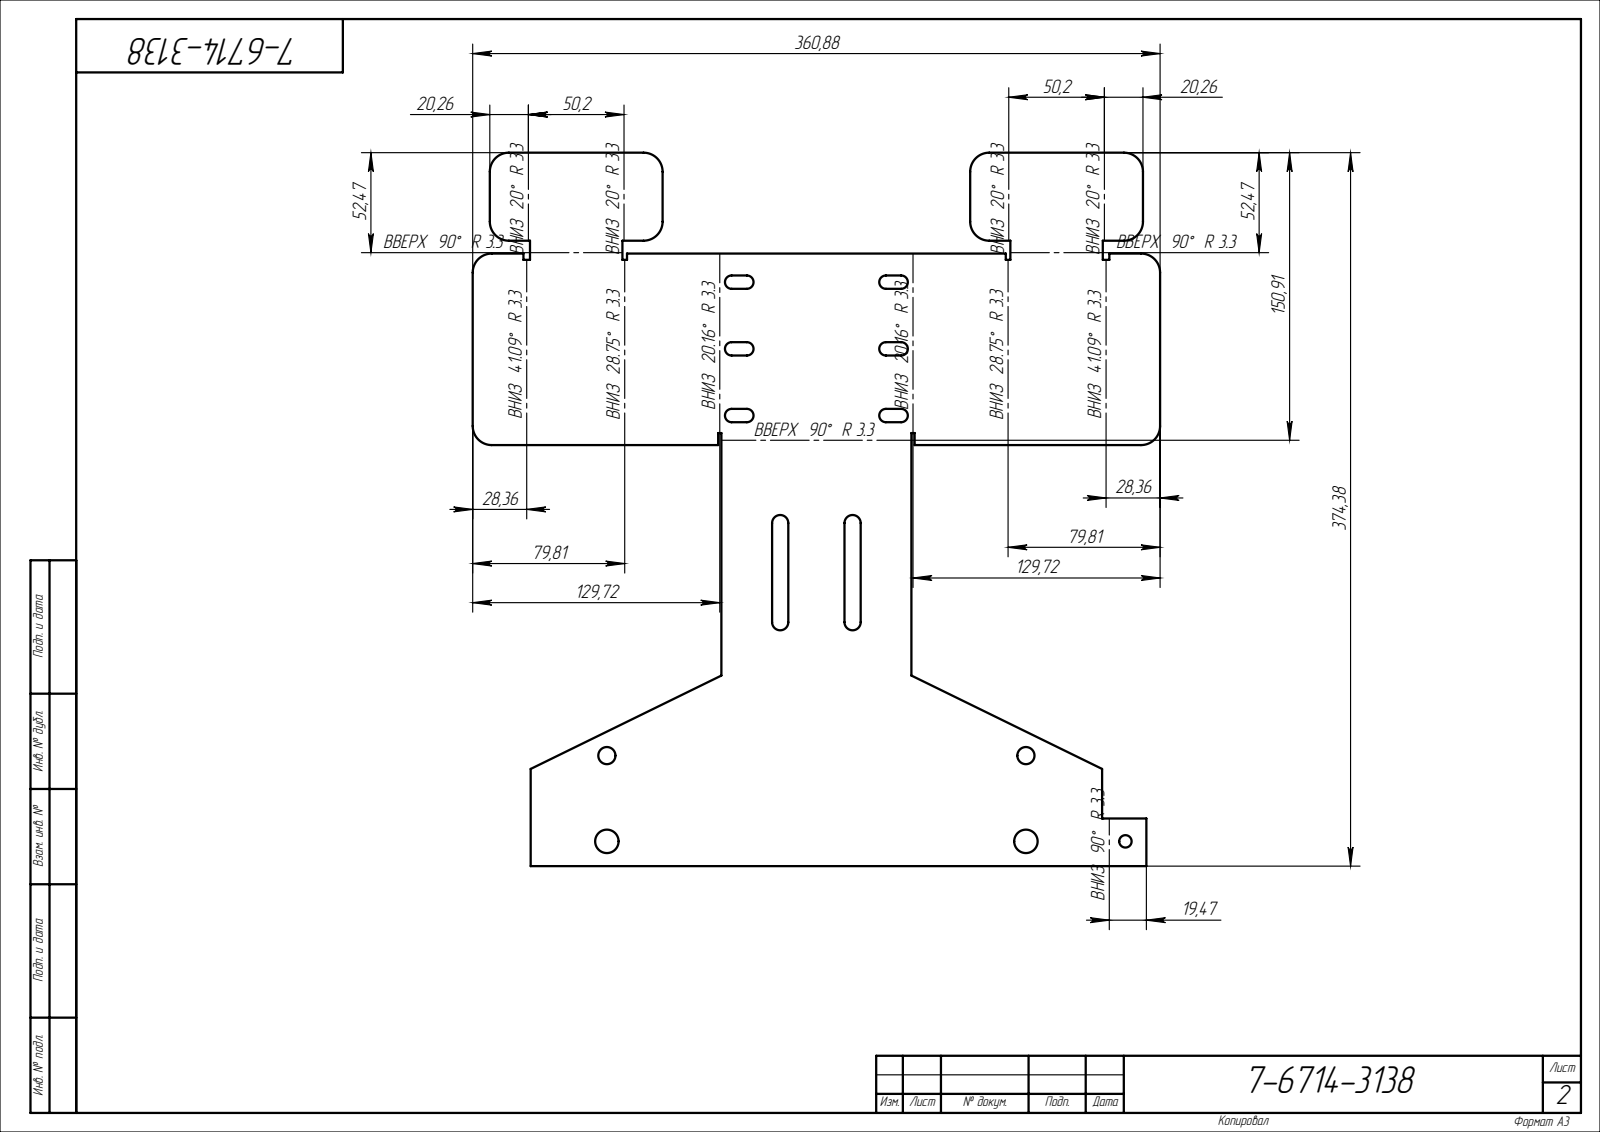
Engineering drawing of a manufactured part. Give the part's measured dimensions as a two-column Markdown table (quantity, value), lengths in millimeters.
| quantity | value |
| --- | --- |
| part name | 7-6714-3138 Основание подвижной каретки |
| STEP written by | SolidWorks 2021 (AUTOMOTIVE_DESIGN) |
| units | millimeters |
| bodies | 1 solid, 195 faces (121 planar, 74 cylindrical, 0 other) |
| overall size | 360.16 × 309 × 129.34 |
| volume | 242 293 mm³ |
| surface area | 169 810 mm² |
| round holes (diameter × count) | 9 × 2, 12.3 × 2, 6.5 × 1 |
| partial cylindrical surfaces (radius × count) | 3.3 × 14, 6.3 × 14, 3.5 × 12, 10 × 10, 4.25 × 4 |
| main face-to-face distances | 3, 100.5, 97.5, 263, 3.01, 103.5, 266, 260, 226, 223 |
| hole center spacings | 45, 220, 224.56 |
